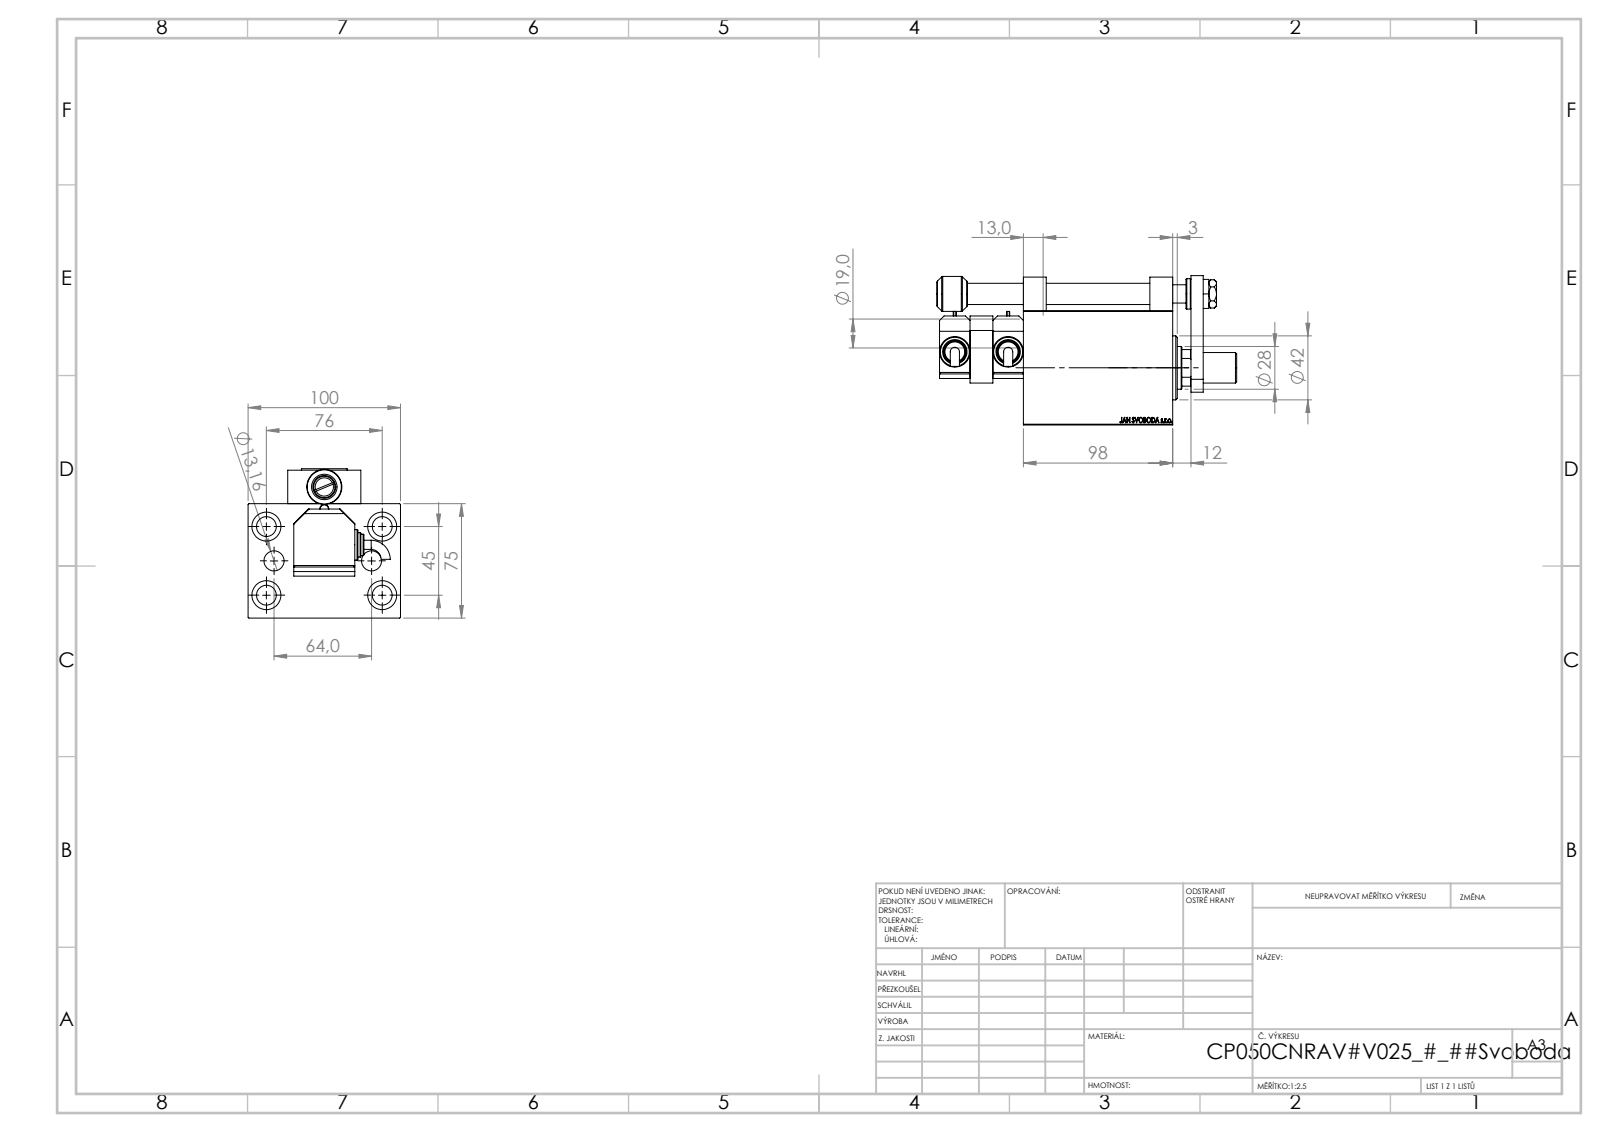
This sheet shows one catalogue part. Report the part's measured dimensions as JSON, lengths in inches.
{"part_name": "SWITCH_P_FRONT_BACK; SWITCH DIM W_B; V450CM_VC_B; KROUZEK_PRO_TYC (+7 more)", "step_written_by": "SolidWorks 2019 (CONFIG_CONTROL_DESIGN)", "units": "inches", "bodies": {"solids": 15, "faces": 1094, "planar": 523, "cylindrical": 116, "other": 455}, "overall_size": [7.748, 3.937, 3.858], "volume_in3": 49.07, "surface_area_in2": 241.9, "round_holes": [[0.512, 5], [0.157, 4], [0.315, 4], [0.748, 4], [0.518, 2], [0.472, 1], [0.551, 1], [0.728, 1], [0.787, 1], [1.102, 1], [1.24, 1], [1.969, 1]], "round_bosses_or_shafts": [[0.787, 3], [0.63, 2], [0.551, 2], [0.236, 2], [1.654, 1], [0.906, 1], [0.709, 1]], "partial_cylinders_radius": [[0.118, 1], [0.531, 1]], "face_to_face_distances": [2.953, 1.378, 3.937, 0.787, 3.858, 4.646, 0.591, 2.756, 0.472, 1.929], "hole_center_spacings": [1.739, 0.787, 0.907, 0.928, 1.772, 1.813, 2.857, 2.932]}
